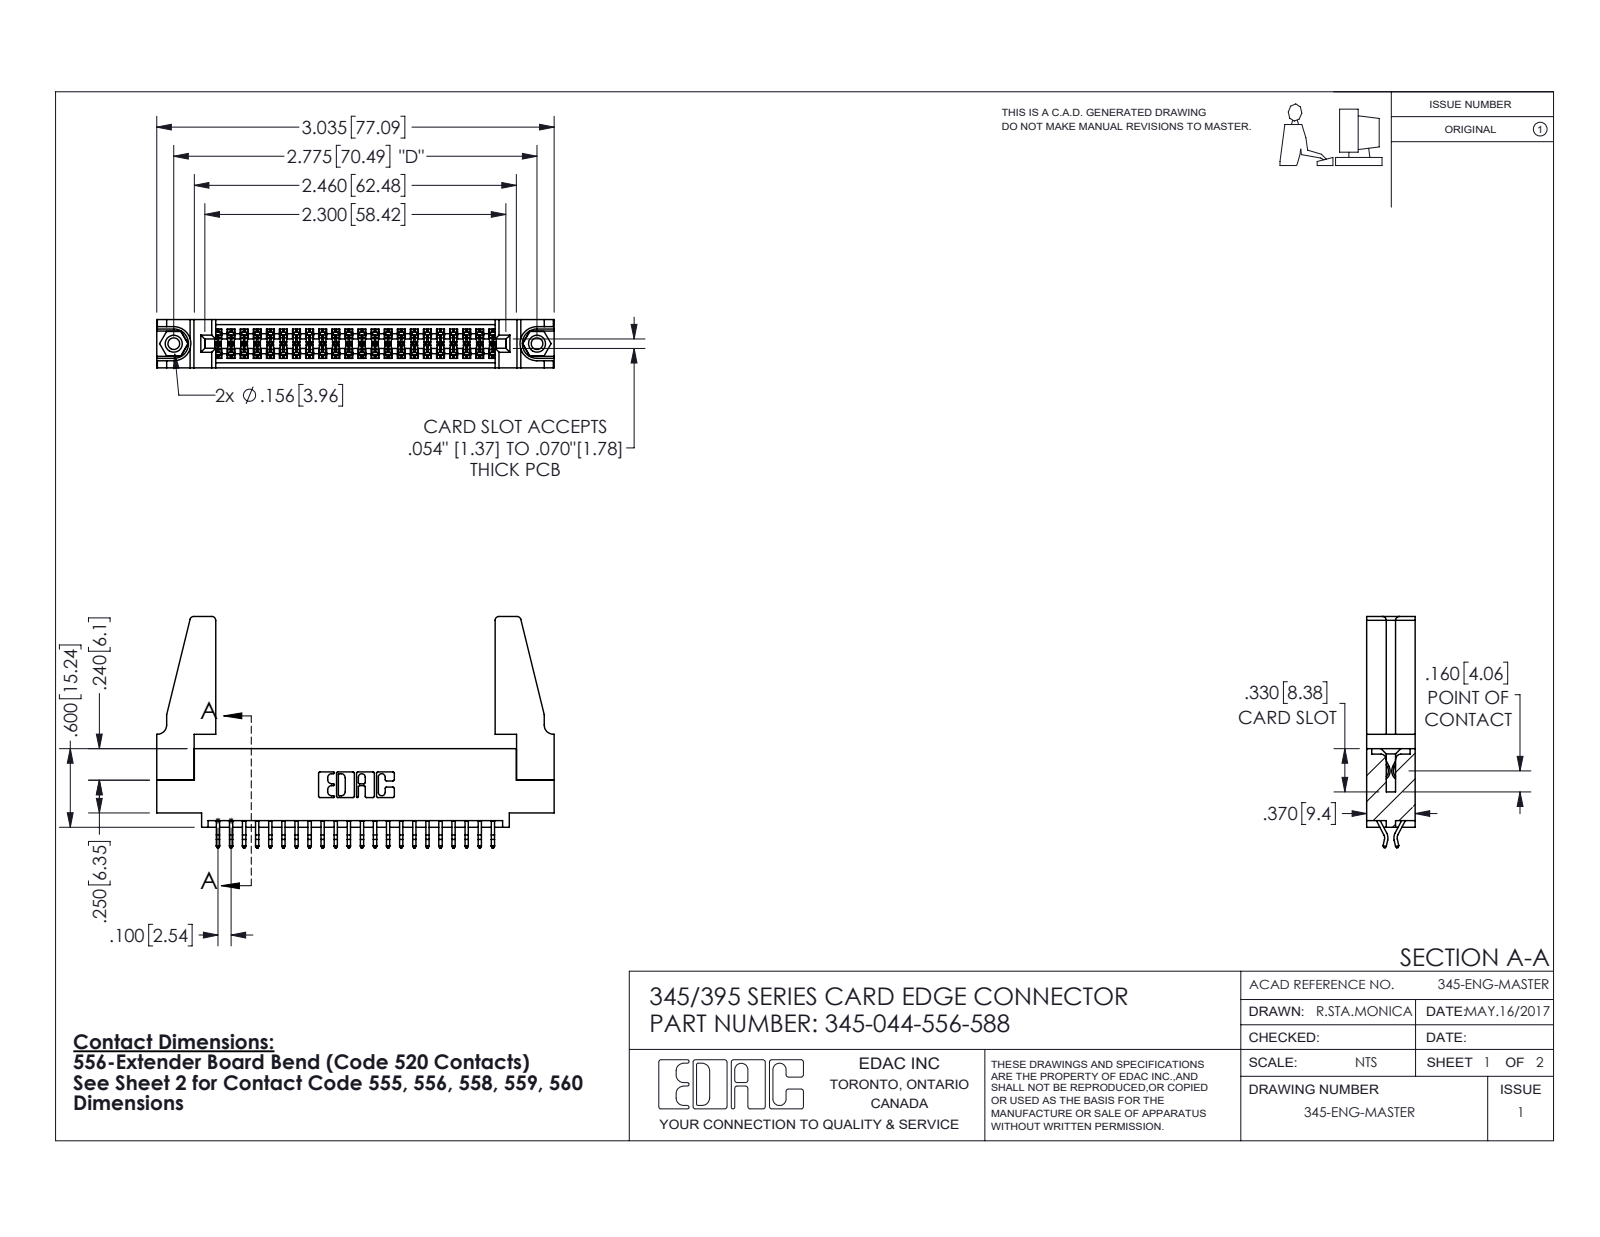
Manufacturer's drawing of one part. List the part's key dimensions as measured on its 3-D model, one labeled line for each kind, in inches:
Part name (STEP PRODUCT): 345-044-556-588; 345-250-001_345-250-001-102; 345-292-001_556 Tail; 345 Part_0.110 Offset - 0.156 Dia-TH (+1 more)
STEP written by: SolidWorks 2016 (CONFIG_CONTROL_DESIGN)
Units: inches
Bodies: 49 solids, 2718 faces (1784 planar, 918 cylindrical, 16 other)
Overall size (bounding box): 3.036 × 1.767 × 0.37
Volume: 0.64 in³ · Surface area: 20.89 in²
Round holes (diameter × count): ⌀0.089 ×2, ⌀0.125 ×2, ⌀0.156 ×2, ⌀0.064 ×1
Round bosses / shafts (diameter × count): ⌀0.155 ×2
Partial cylindrical surfaces — rounded edges, fillets, slot ends (radius × count): R0.006 ×66, R0.01 ×22, R0.03 ×8, R0.007 ×6, R0.031 ×6, R0.026 ×3, R0.01 ×2, R0.014 ×2
Main face-to-face distances: 0.072, 0.37, 0.298, 0.2, 0.025, 0.098, 0.272, 0.225, 0.175, 0.149
Hole centre spacings: 0.27, 2.541, 2.775
